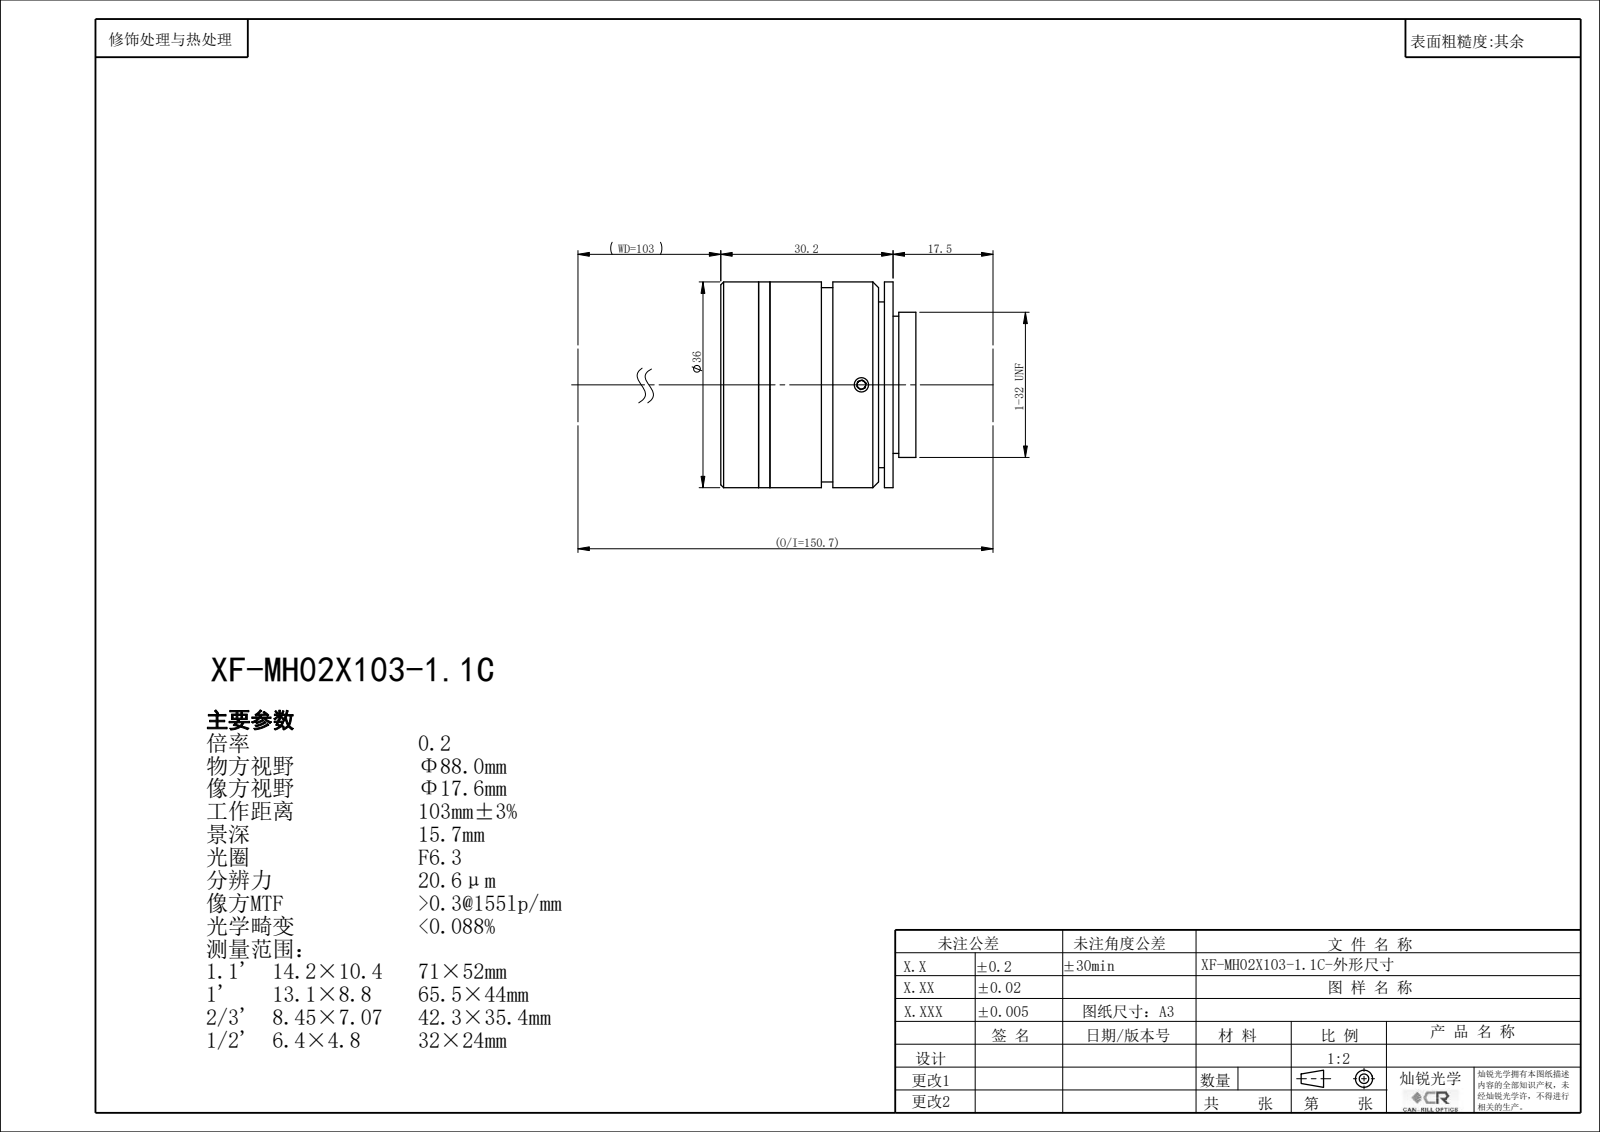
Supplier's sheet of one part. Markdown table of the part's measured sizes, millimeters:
| quantity | value |
| --- | --- |
| part name | XF-MH02X103-1.1C |
| STEP written by | SolidWorks 2022 (CONFIG_CONTROL_DESIGN) |
| units | millimeters |
| bodies | 0 solids, 98 faces (43 planar, 34 cylindrical, 21 other) |
| overall size | 36 × 36 × 34.16 |
| round holes (diameter × count) | 2.5 × 3, 10 × 1, 15 × 1, 17.4 × 1, 21.5 × 1, 24.9 × 1, 26 × 1 |
| round bosses / shafts (diameter × count) | 36 × 1, 34 × 1, 25.4 × 1, 24 × 1 |
| main face-to-face distances | 2, 23.54, 21.54, 6.62, 8.62, 30.16, 1.5, 28.66, 22.04, 20.04 |
